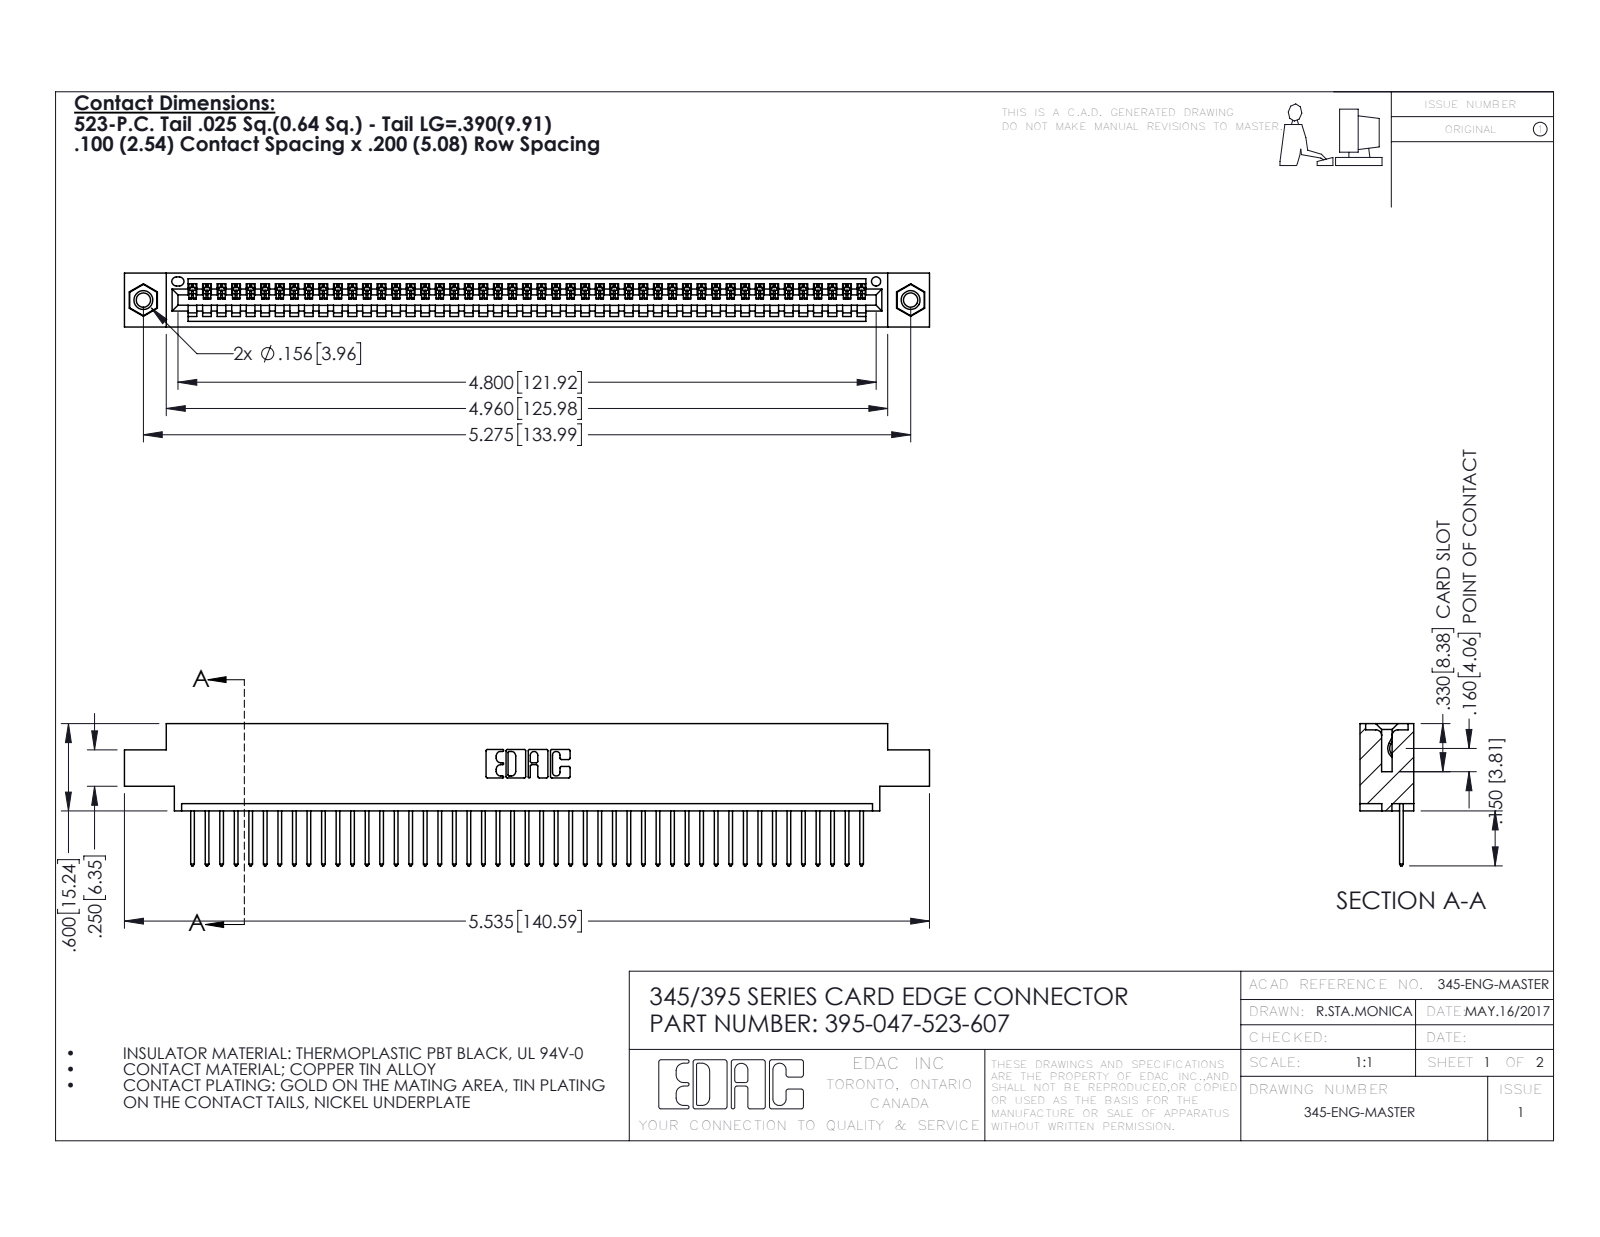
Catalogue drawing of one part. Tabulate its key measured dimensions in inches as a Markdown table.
| quantity | value |
| --- | --- |
| part name | 345-292-001_345-293-123; 395-047-523-607; 345-250-001_345-250-005-103; 345 Part_0.170 Offset - 0.156 Dia-TI |
| STEP written by | SolidWorks 2016 (CONFIG_CONTROL_DESIGN) |
| units | inches |
| bodies | 50 solids, 2916 faces (1996 planar, 904 cylindrical, 16 other) |
| overall size | 5.535 × 0.977 × 0.37 |
| volume | 0.809 in³ |
| surface area | 27.72 in² |
| round holes (diameter × count) | 0.098 × 2, 0.125 × 2, 0.156 × 2, 0.064 × 1 |
| round bosses / shafts (diameter × count) | 0.155 × 2 |
| partial cylindrical surfaces (radius × count) | 0.006 × 94, 0.01 × 94, 0.01 × 22, 0.007 × 6, 0.031 × 6, 0.026 × 3, 0.031 × 2, 0.04 × 2 |
| main face-to-face distances | 0.072, 0.298, 0.37, 0.2, 0.098, 0.272, 0.025, 0.225, 0.175, 0.149 |
| hole center spacings | 0.27, 5.039, 5.275 |
